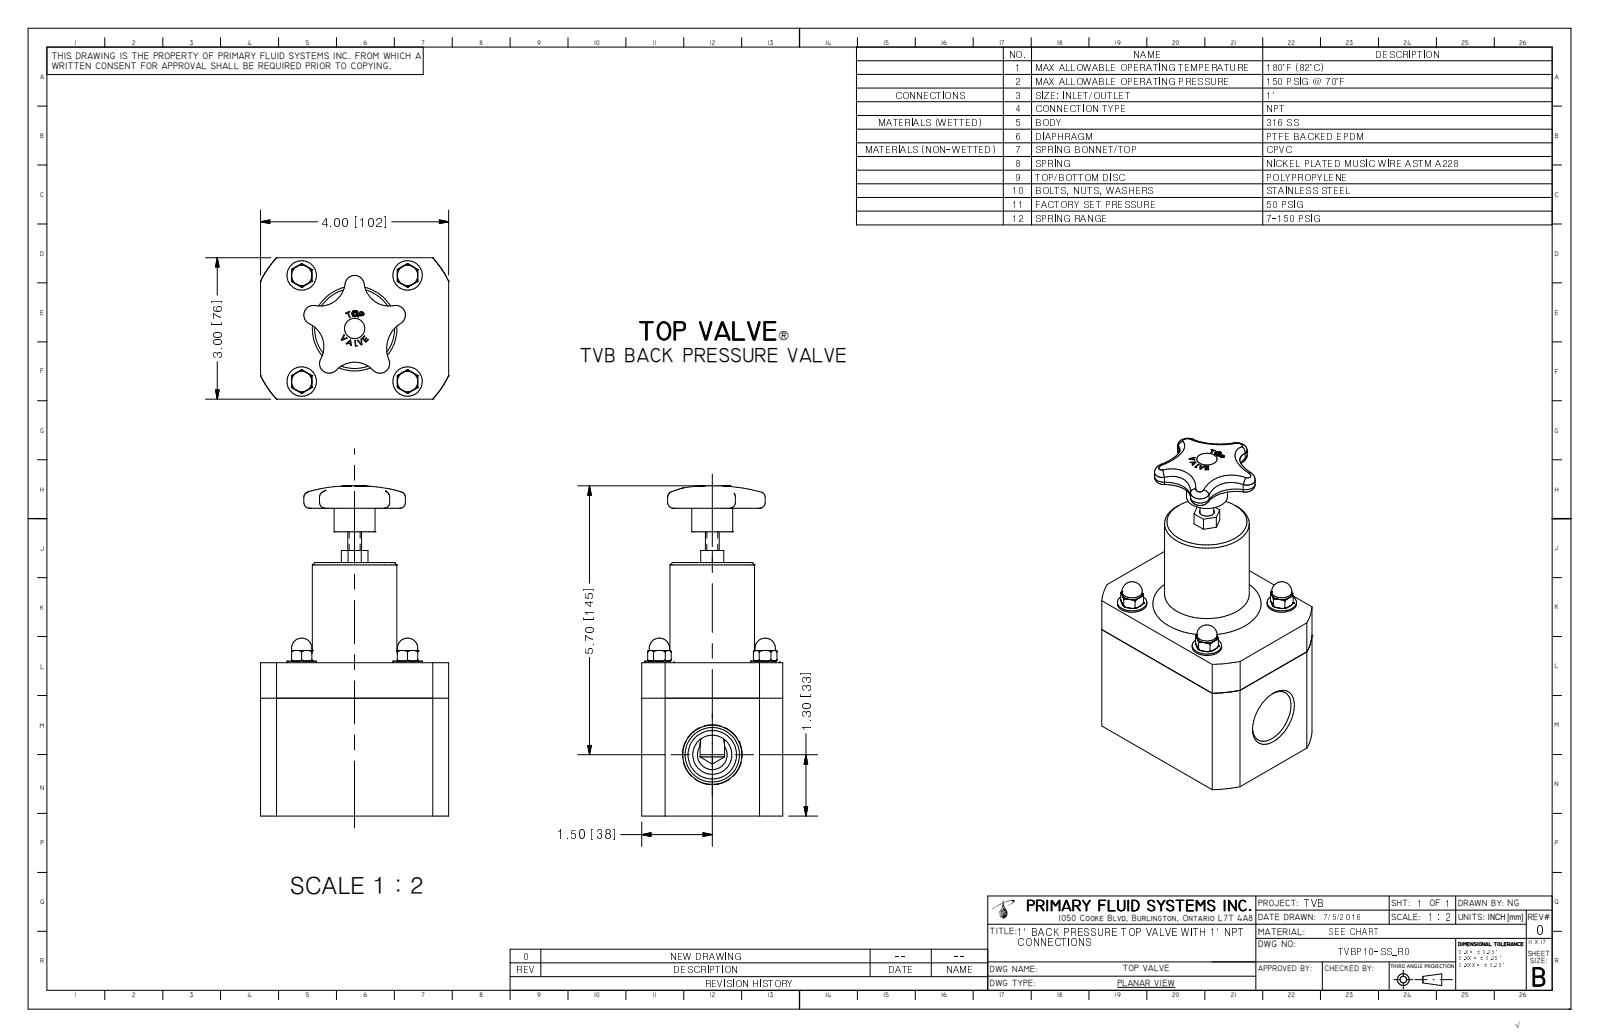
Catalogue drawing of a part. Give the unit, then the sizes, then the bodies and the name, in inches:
Units: inches
Overall size (bounding box): 7.002 × 4 × 3
Round holes (diameter × count): ⌀0.175 ×4, ⌀1.156 ×1
Round bosses / shafts (diameter × count): ⌀0.625 ×4, ⌀0.433 ×4, ⌀0.375 ×4, ⌀1.8 ×1, ⌀0.87 ×1, ⌀0.293 ×1
Partial cylindrical surfaces — rounded edges, fillets, slot ends (radius × count): R0.085 ×5, R0.205 ×5, R0.536 ×4, R0.656 ×4, R0.625 ×1, R0.745 ×1, R2.238 ×1, R2.238 ×1
Main face-to-face distances: 3, 3.25, 4, 1, 5.375, 2.125, 2, 3.286, 0.036, 2.089
Hole centre spacings: 2.25, 3.182
Volume: 42.84 in³ · Surface area: 100.4 in²
Bodies: 1 solid, 345 faces (148 planar, 49 cylindrical, 148 other)
Part name (STEP PRODUCT): TVBP10-SS-R0
STEP written by: Autodesk Inventor 2009 (AUTOMOTIVE_DESIGN)
